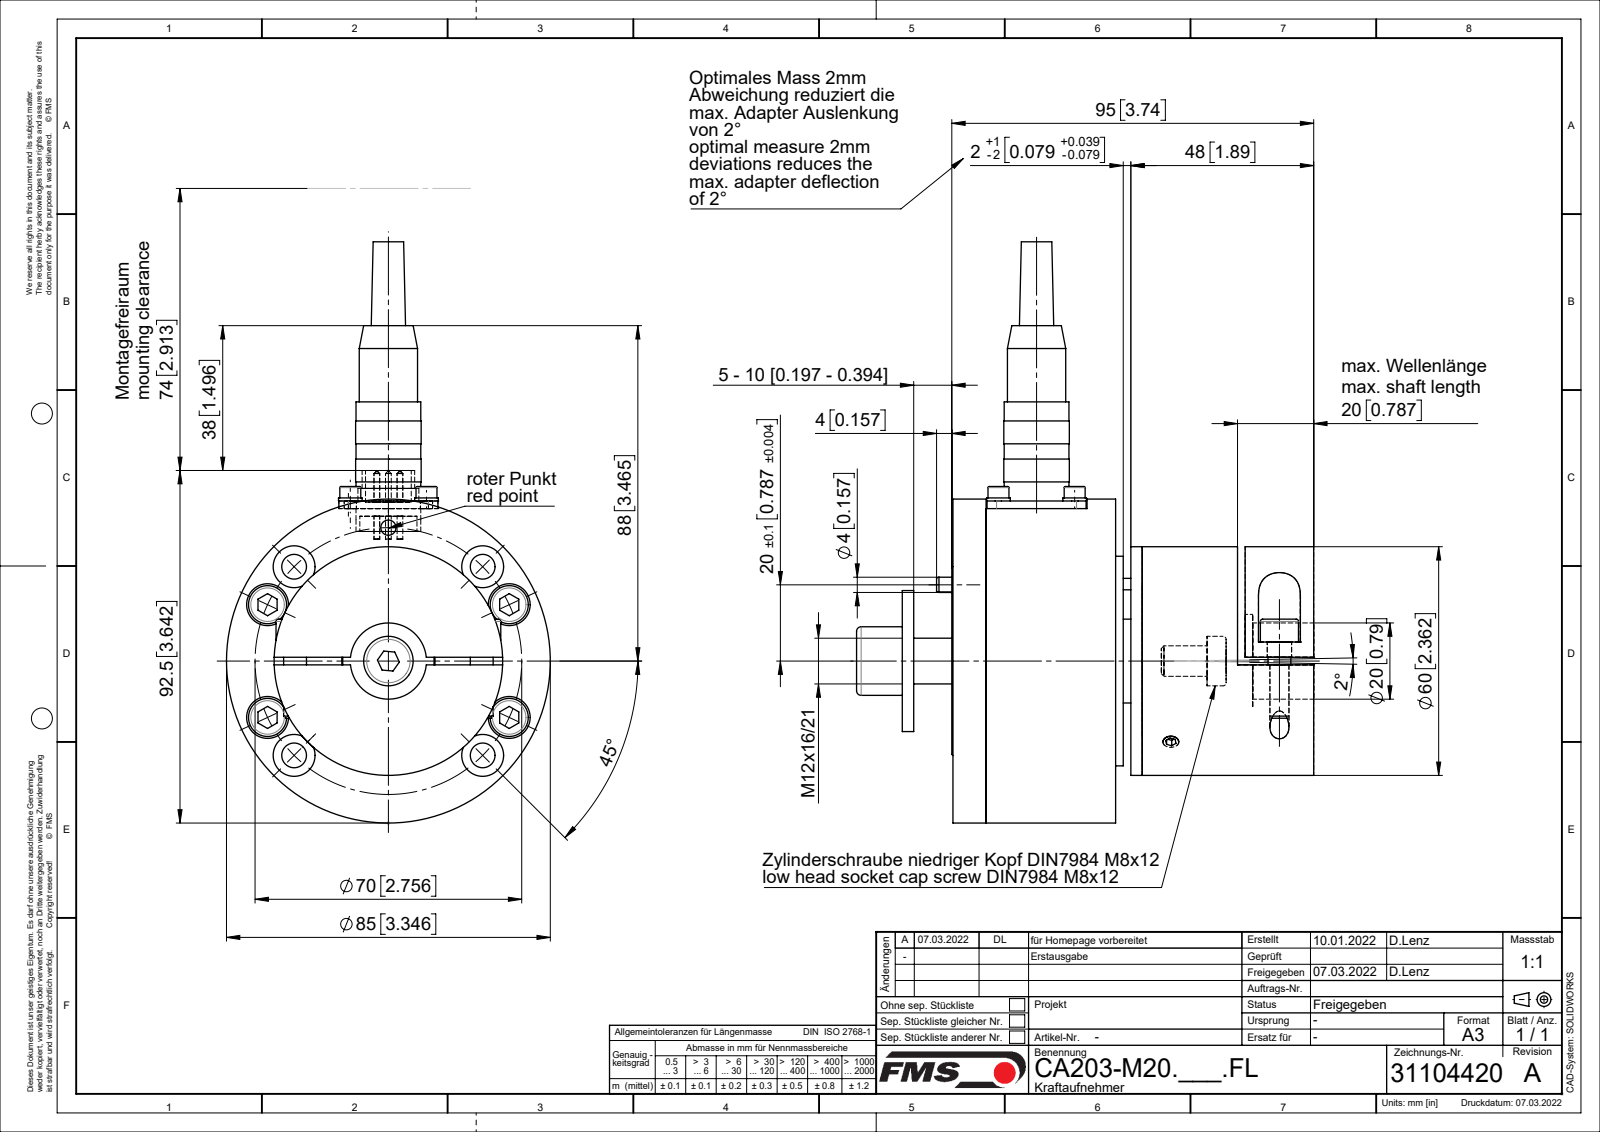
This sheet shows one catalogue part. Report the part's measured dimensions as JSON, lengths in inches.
{"part_name": "Kabeldose_M14x1_Mini_5pol; Zyl-Schr DIN912_M6x30; Federringe_DIN127A_M03; Zyl-Schr DIN912_M3x6 (+8 more)", "step_written_by": "SolidWorks 2018 (CONFIG_CONTROL_DESIGN)", "units": "inches", "bodies": {"solids": 43, "faces": 792, "planar": 272, "cylindrical": 331, "other": 189}, "overall_size": [6.004, 4.724, 3.346], "volume_in3": 19.24, "surface_area_in2": 173.6, "round_holes": [[0.098, 8], [0.256, 8], [0.433, 8], [0.197, 6], [0.157, 5], [0.122, 4], [0.126, 4], [0.142, 4], [0.276, 4], [0.118, 2], [0.252, 2], [0.165, 1]], "round_bosses_or_shafts": [[0.118, 8], [0.236, 7], [0.394, 6], [0.059, 5], [0.244, 4], [0.224, 4], [0.217, 4], [3.346, 1]], "partial_cylinders_radius": [[0.098, 4], [0.197, 2], [0.217, 2]], "face_to_face_distances": [0.079, 1.614, 1.772, 0.394, 1.181, 0.118, 1.969, 0.866, 2.362, 1.339], "hole_center_spacings": [1.378, 0.787, 0.976, 0.992, 1.291, 2.013, 2.223, 1.113]}
